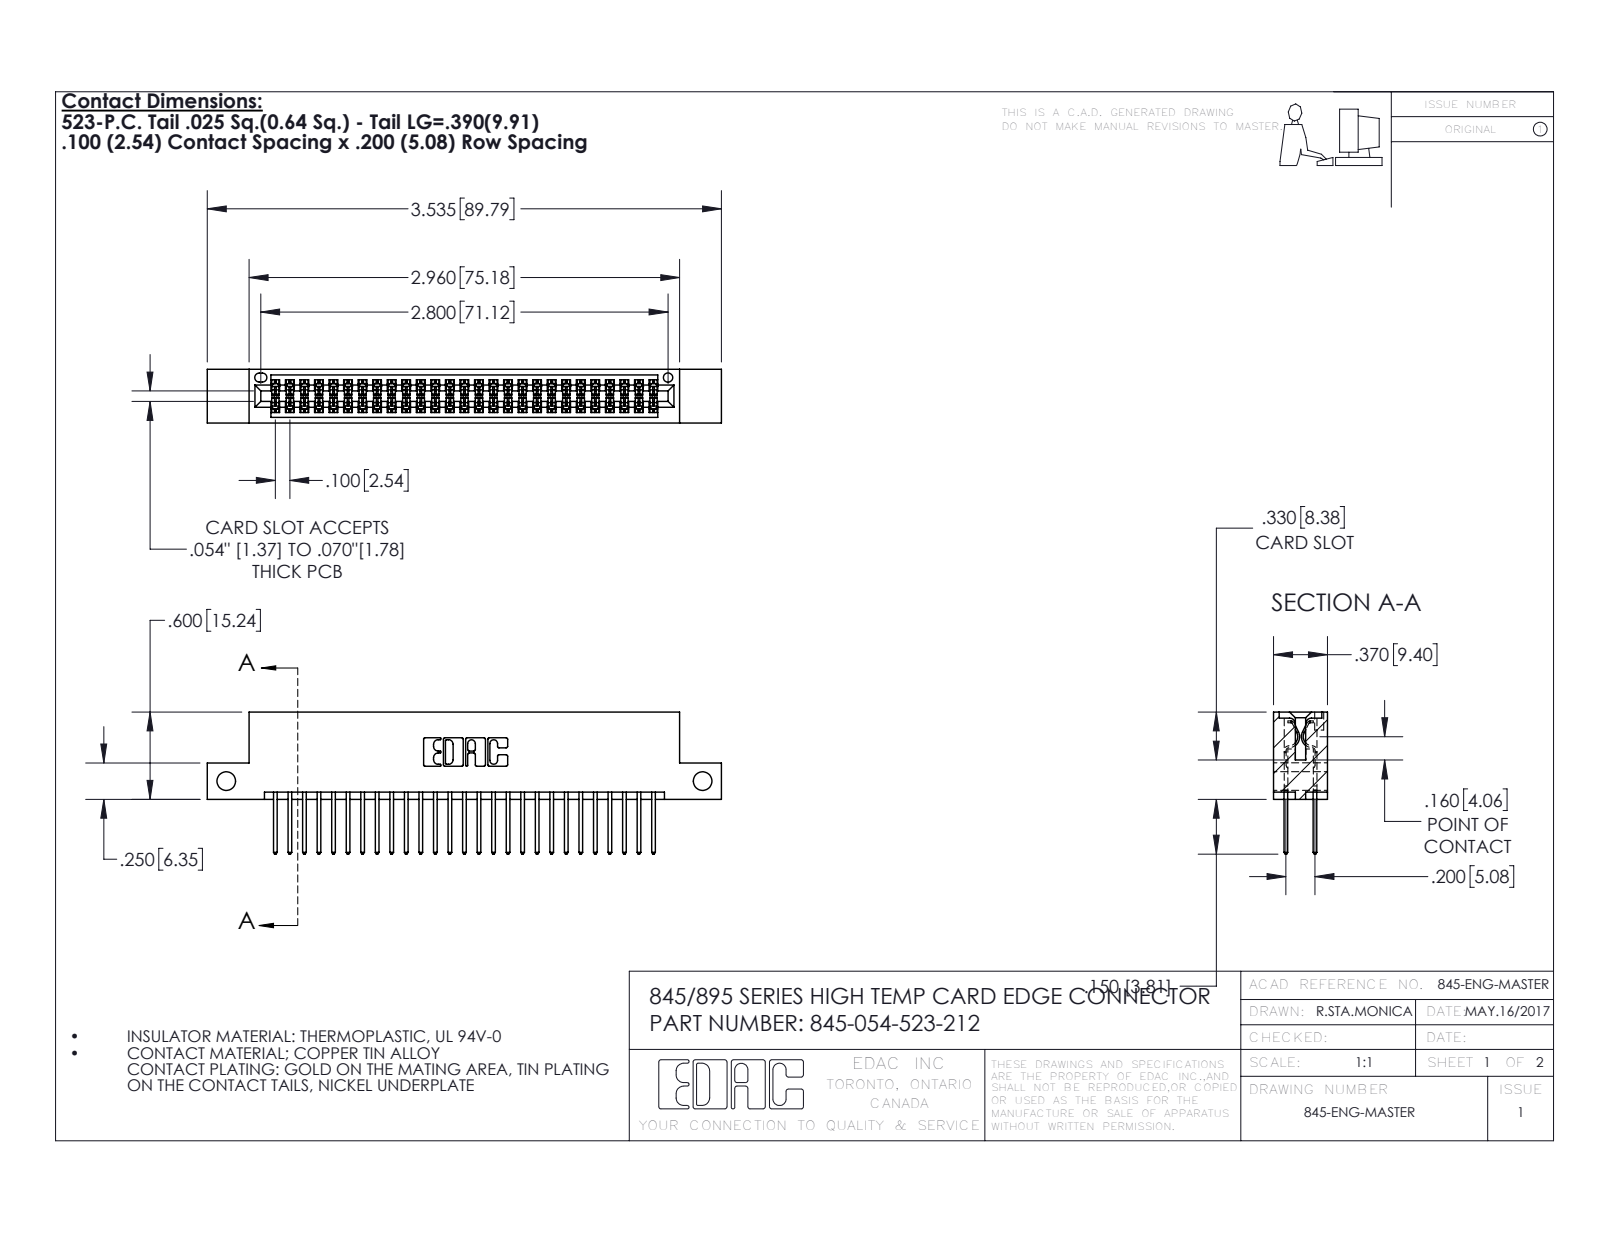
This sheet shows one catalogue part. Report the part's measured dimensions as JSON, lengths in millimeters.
{"part_name": "345 Part_Flush Mounting Lugs - Side Mount; 345-292-001_345-293-123; 345-054-523-212", "step_written_by": "SolidWorks 2016 (CONFIG_CONTROL_DESIGN)", "units": "millimeters", "bodies": {"solids": 31, "faces": 1818, "planar": 1238, "cylindrical": 580, "other": 0}, "overall_size": [89.8, 24.8, 9.4], "volume_mm3": 8340, "surface_area_mm2": 10950, "round_holes": [[3.3, 2], [1.6, 1]], "partial_cylinders_radius": [[0.2, 57], [0.3, 54], [0.3, 22], [0.2, 6], [0.8, 6], [0.7, 3], [0.4, 2], [0.5, 2]], "face_to_face_distances": [7.6, 1.8, 5.1, 9.4, 2.5, 6.9, 0.6, 5.7, 3.8, 1.8], "hole_center_spacings": [83.2]}
